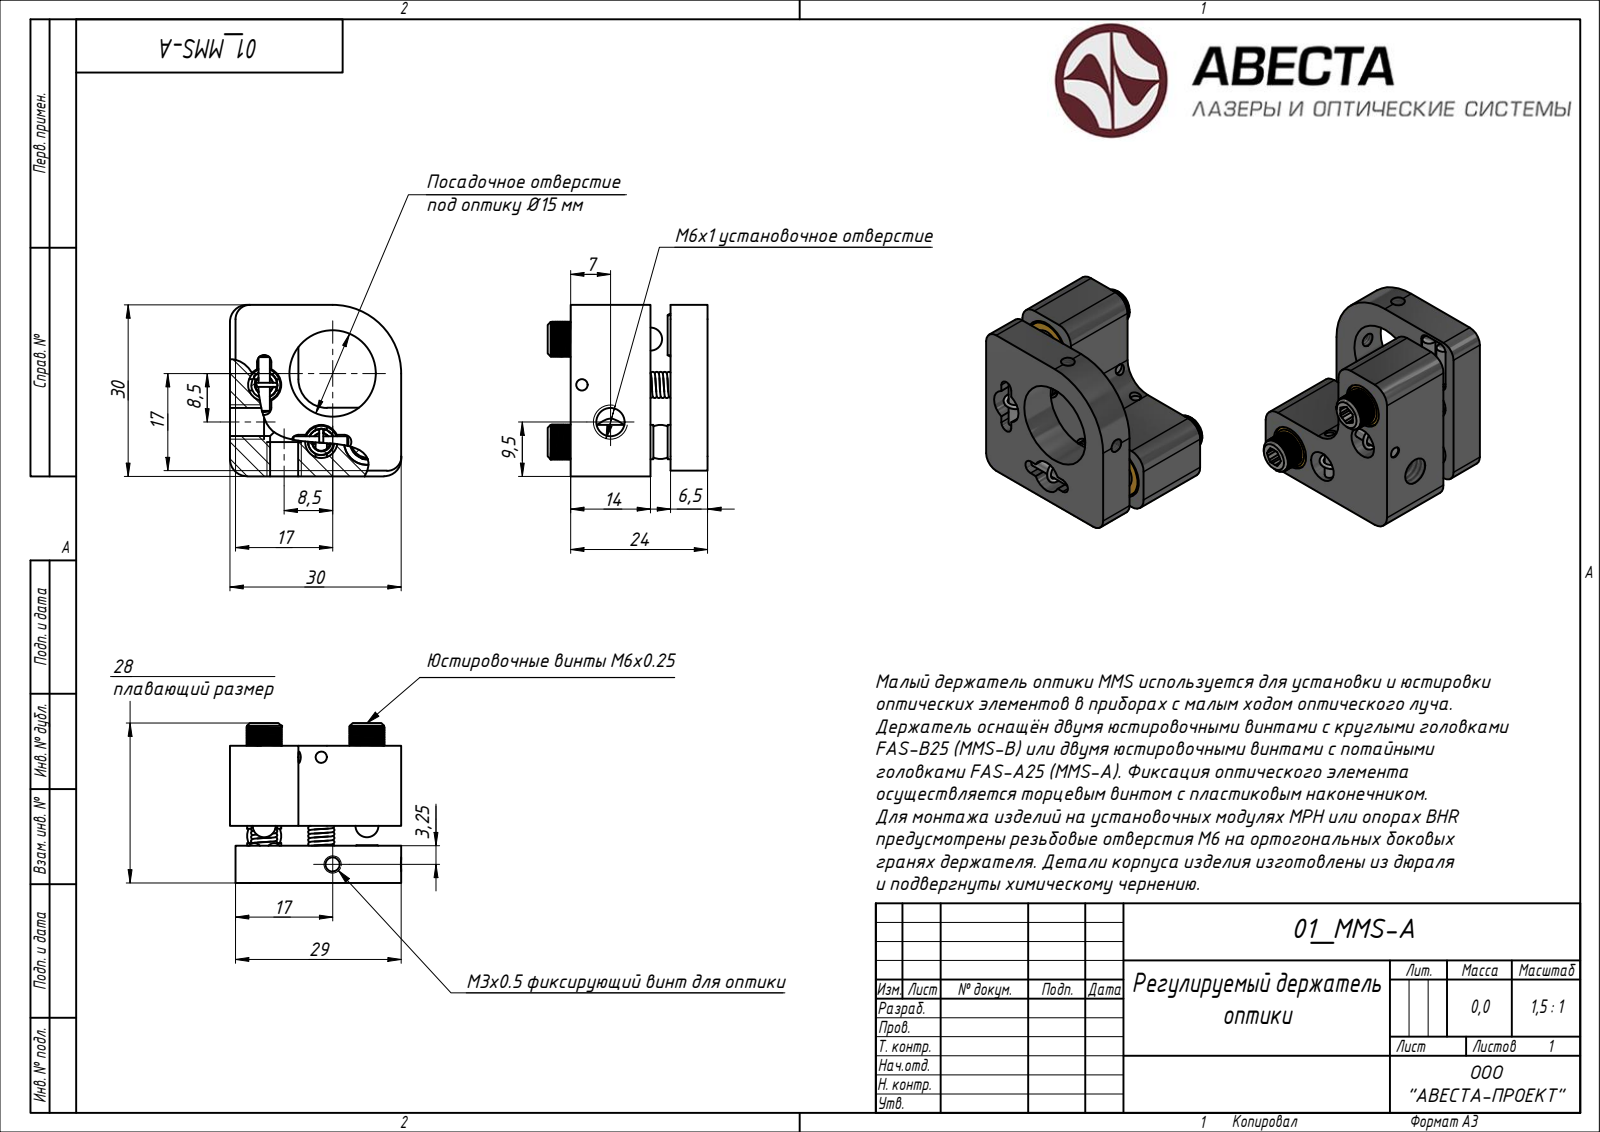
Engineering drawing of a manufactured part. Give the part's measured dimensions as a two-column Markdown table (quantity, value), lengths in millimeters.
| quantity | value |
| --- | --- |
| STEP written by | ST-DEVELOPER v15 (AUTOMOTIVE_DESIGN) |
| units | millimeters |
| bodies | 20 solids, 297 faces (92 planar, 0 cylindrical, 205 other) |
| overall size | 30 × 30 × 24.6 |
| volume | 10 847 mm³ |
| surface area | 9 810 mm² |
| main face-to-face distances | 6.5, 3.5, 24, 17.5, 10, 14, 1, 12, 30, 11 |
